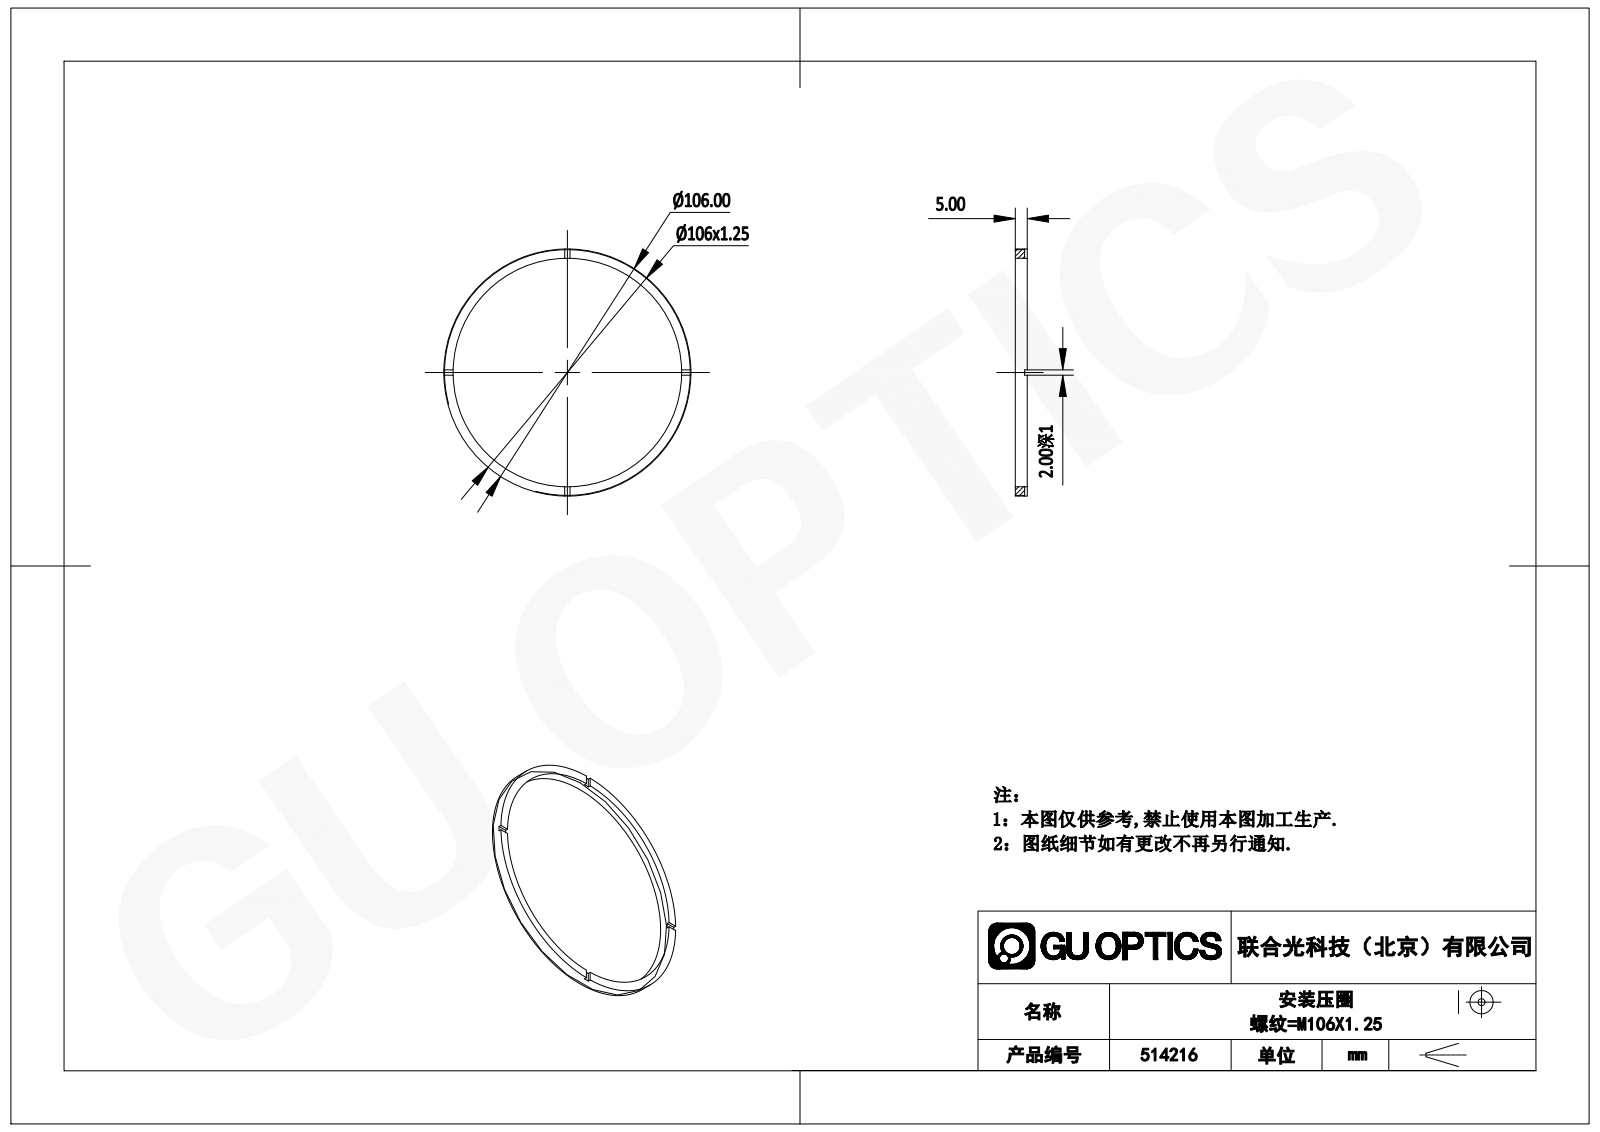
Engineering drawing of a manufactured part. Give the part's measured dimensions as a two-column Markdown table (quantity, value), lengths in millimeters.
| quantity | value |
| --- | --- |
| part name | 514216 |
| STEP written by | SolidWorks 2020 (CONFIG_CONTROL_DESIGN) |
| units | millimeters |
| bodies | 1 solid, 21 faces (17 planar, 4 cylindrical, 0 other) |
| overall size | 106 × 106 × 5 |
| volume | 6 377 mm³ |
| surface area | 5 784 mm² |
| round holes (diameter × count) | 98 × 1 |
| round bosses / shafts (diameter × count) | 106 × 1 |
| main face-to-face distances | 5, 4, 1, 2 |
